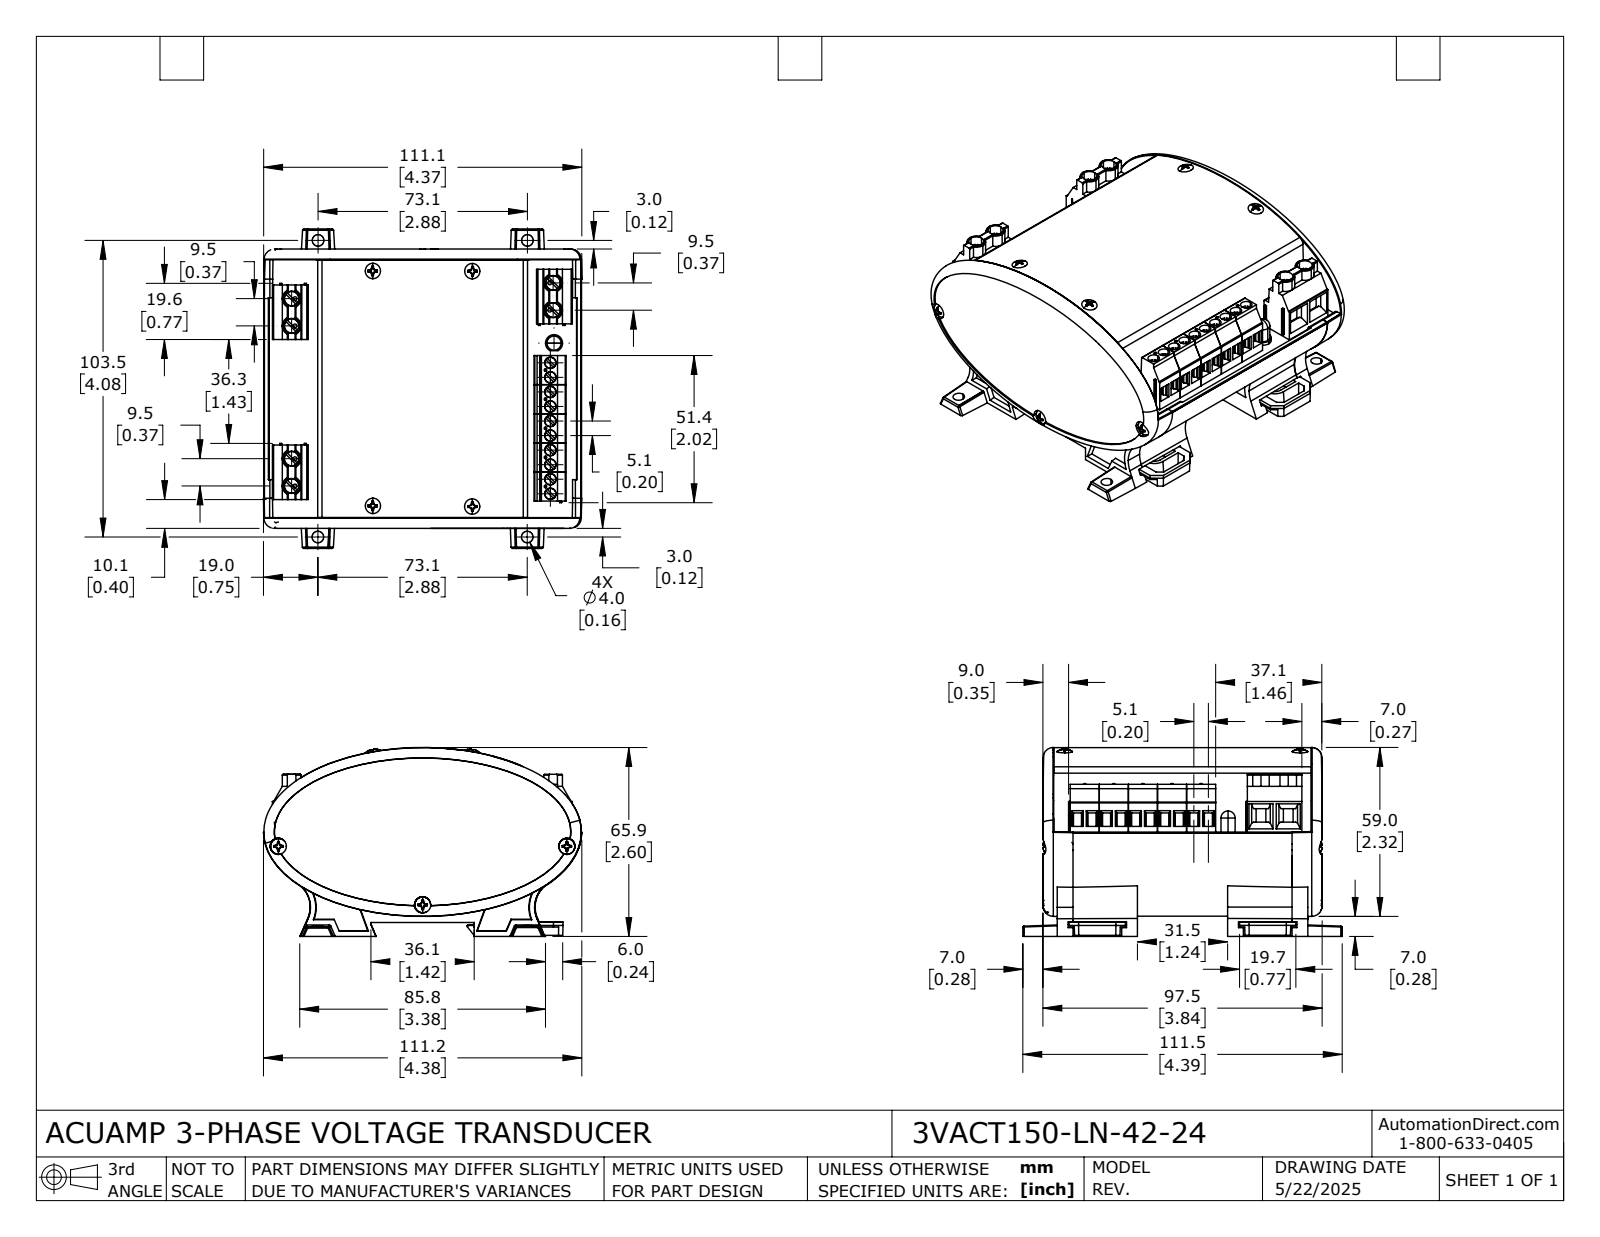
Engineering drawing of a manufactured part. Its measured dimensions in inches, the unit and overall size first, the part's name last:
Units: inches
Overall size (bounding box): 4.391 × 4.377 × 2.597
Round holes (diameter × count): ⌀0.05 ×12, ⌀0.157 ×10, ⌀0.08 ×6, ⌀0.111 ×6, ⌀0.205 ×6, ⌀0.126 ×4
Round bosses / shafts (diameter × count): ⌀0.051 ×16, ⌀0.15 ×10, ⌀0.112 ×10, ⌀0.067 ×10, ⌀0.197 ×6, ⌀0.018 ×4, ⌀0.234 ×1, ⌀0.194 ×1
Partial cylindrical surfaces — rounded edges, fillets, slot ends (radius × count): R0.006 ×40, R0.039 ×20, R0.008 ×16, R0.02 ×16, R0.01 ×6, R0.012 ×6, R0.128 ×6, R0.018 ×4
Main face-to-face distances: 0.063, 0.128, 3.672, 3.8, 3.543, 0.084, 0.394, 3.406, 0.266, 3.278
Hole centre spacings: 0.2, 0.4, 0.6, 0.8, 1, 1.2, 1.4, 1.6
Volume: 8.539 in³ · Surface area: 197.4 in²
Bodies: 26 solids, 2965 faces (1484 planar, 838 cylindrical, 643 other)
Part name (STEP PRODUCT): 3VACT150-LN-42-24
STEP written by: SolidWorks 2024 (AUTOMOTIVE_DESIGN)
